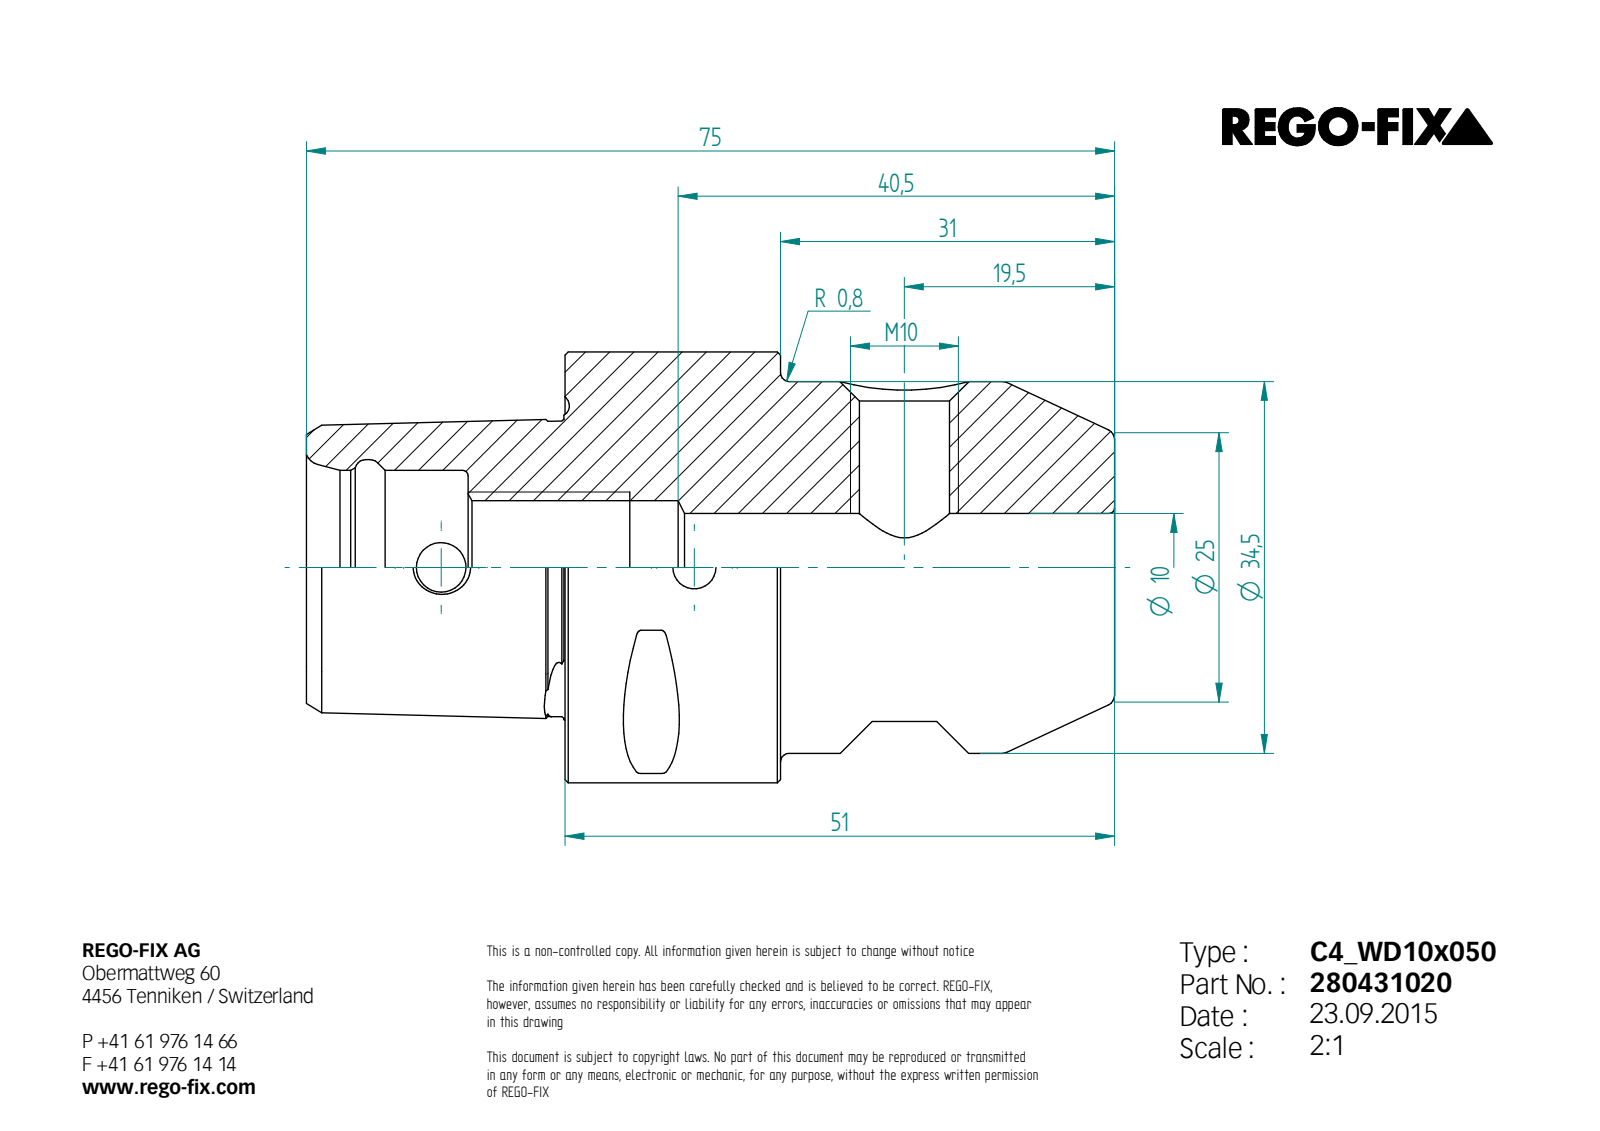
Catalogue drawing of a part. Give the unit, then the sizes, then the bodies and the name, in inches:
Units: inches
Overall size (bounding box): 2.953 × 1.575 × 1.575
Round holes (diameter × count): ⌀0.157 ×1, ⌀0.181 ×1, ⌀0.33 ×1, ⌀0.394 ×1, ⌀0.487 ×1, ⌀0.709 ×1, ⌀0.787 ×1
Round bosses / shafts (diameter × count): ⌀1.575 ×1, ⌀1.358 ×1
Partial cylindrical surfaces — rounded edges, fillets, slot ends (radius × count): R0.02 ×8
Main face-to-face distances: 2.008, 0.787, 1.22, 0.945, 1.732, 2.953, 0.611, 0.591, 0.354, 1.142
Hole centre spacings: 0.925
Volume: 3.321 in³ · Surface area: 20.04 in²
Bodies: 1 solid, 105 faces (23 planar, 20 cylindrical, 62 other)
STEP written by: Unknown (AUTOMOTIVE_DESIGN)
